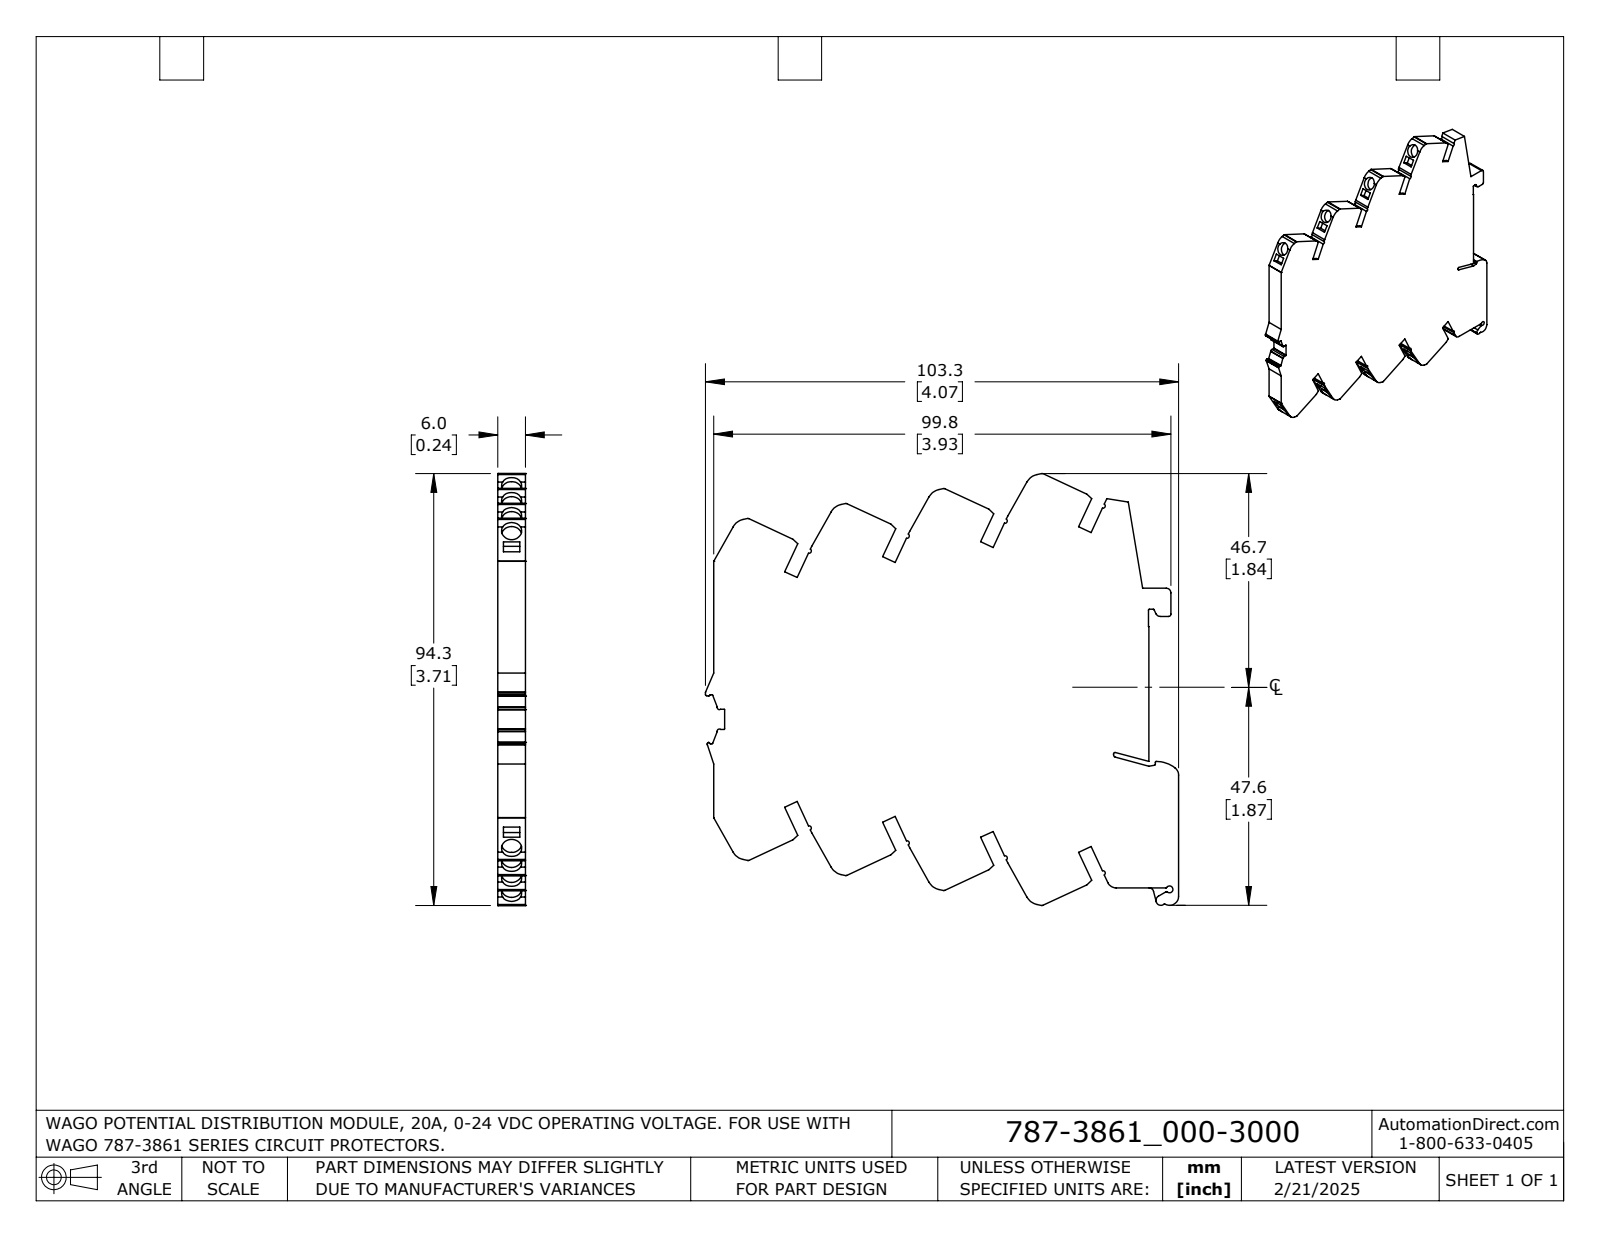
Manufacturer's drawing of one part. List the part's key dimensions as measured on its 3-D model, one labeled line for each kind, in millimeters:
Part name (STEP PRODUCT): 787-3861_000-3000_HI
STEP written by: SolidWorks 2024 (AUTOMOTIVE_DESIGN)
Units: millimetres
Bodies: 1 solid, 255 faces (191 planar, 64 cylindrical, 0 other)
Overall size (bounding box): 103.3 × 94.26 × 6
Volume: 44 000 mm³ · Surface area: 18 850 mm²
Round holes (diameter × count): ⌀4.4 ×8
Partial cylindrical surfaces — rounded edges, fillets, slot ends (radius × count): R0.2 ×13, R0.5 ×12, R0.4 ×8, R3.35 ×8, R1 ×5, R0.3 ×3, R2 ×3, R0.45 ×2
Main face-to-face distances: 6, 17.99, 17.02, 35.98, 3, 12.01, 20.99, 12, 34.04, 38.98
Hole centre spacings: 13.35, 13.34, 26.7, 26.71, 40.05
